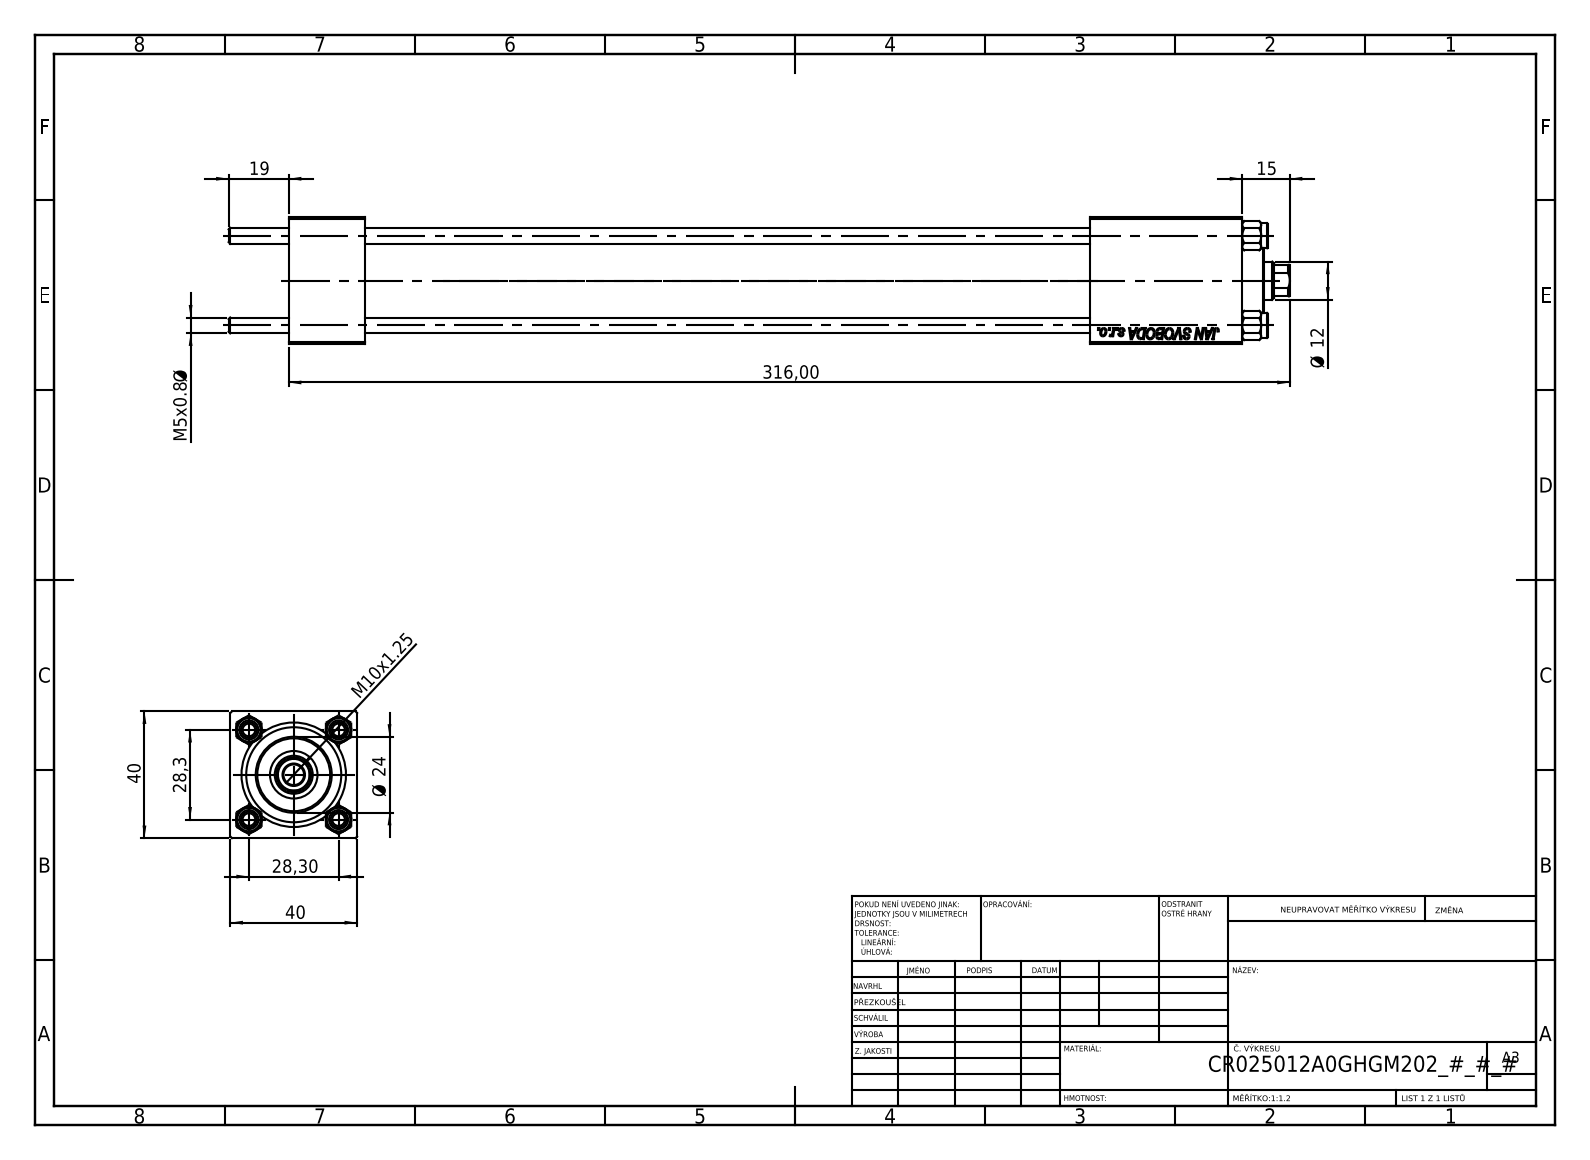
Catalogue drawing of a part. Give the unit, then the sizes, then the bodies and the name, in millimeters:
Units: millimetres
Overall size (bounding box): 335 × 40 × 40
Round holes (diameter × count): ⌀5 ×4, ⌀20 ×3, ⌀7 ×2, ⌀13.16 ×2, ⌀6.5 ×1, ⌀12 ×1, ⌀15 ×1, ⌀25 ×1, ⌀30 ×1
Round bosses / shafts (diameter × count): ⌀8 ×4, ⌀31 ×1, ⌀24 ×1
Partial cylindrical surfaces — rounded edges, fillets, slot ends (radius × count): R5.5 ×1
Main face-to-face distances: 40, 24, 301, 277, 272.3, 248.3, 28.7, 253, 229, 19.3
Hole centre spacings: 20.01, 28.3, 40.02, 254
Volume: 227 731 mm³ · Surface area: 109 187 mm²
Bodies: 11 solids, 1131 faces (517 planar, 78 cylindrical, 536 other)
Part name (STEP PRODUCT): CR025_012_A_0_G_A_G_M_020_+#_##_TYCINKA; NUT_M5; V215_VC_A; V215CR_VCP (+1 more)
STEP written by: SolidWorks 2019 (CONFIG_CONTROL_DESIGN)
